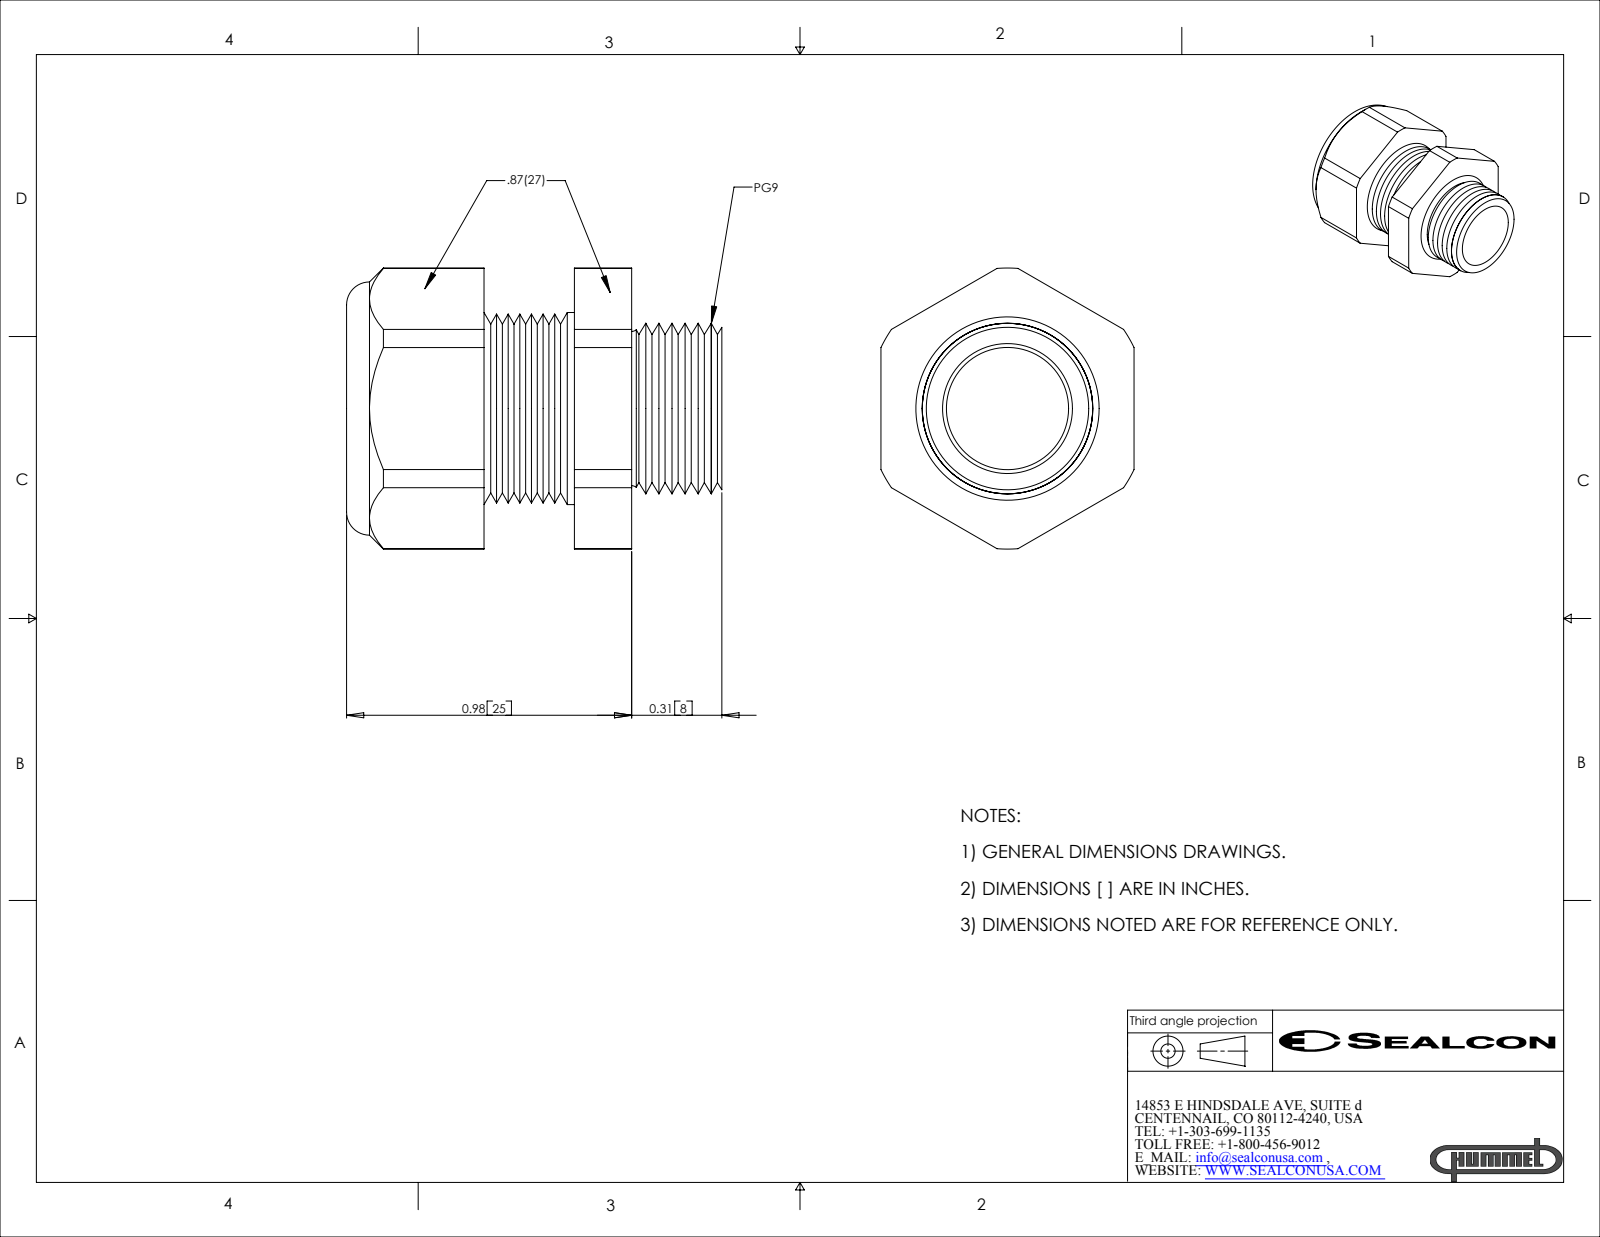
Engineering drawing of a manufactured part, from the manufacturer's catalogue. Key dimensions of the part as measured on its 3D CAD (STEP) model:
Part name (STEP PRODUCT): CD09GA-GY
STEP written by: SolidWorks 2007 (CONFIG_CONTROL_DESIGN)
Units: inches
Bodies: 2 solids, 116 faces (20 planar, 22 cylindrical, 74 other)
Overall size (bounding box): 1.29 × 0.966 × 0.87
Volume: 0.404 in³ · Surface area: 9.399 in²
Round holes (diameter × count): ⌀0.42 ×1, ⌀0.6 ×1
Round bosses / shafts (diameter × count): ⌀0.66 ×1
Partial cylindrical surfaces — rounded edges, fillets, slot ends (radius × count): R0.483 ×1
Main face-to-face distances: 0.87, 0.508, 0.311, 0.197, 0.472, 0.783, 0.98, 0.03, 0.442, 0.753
